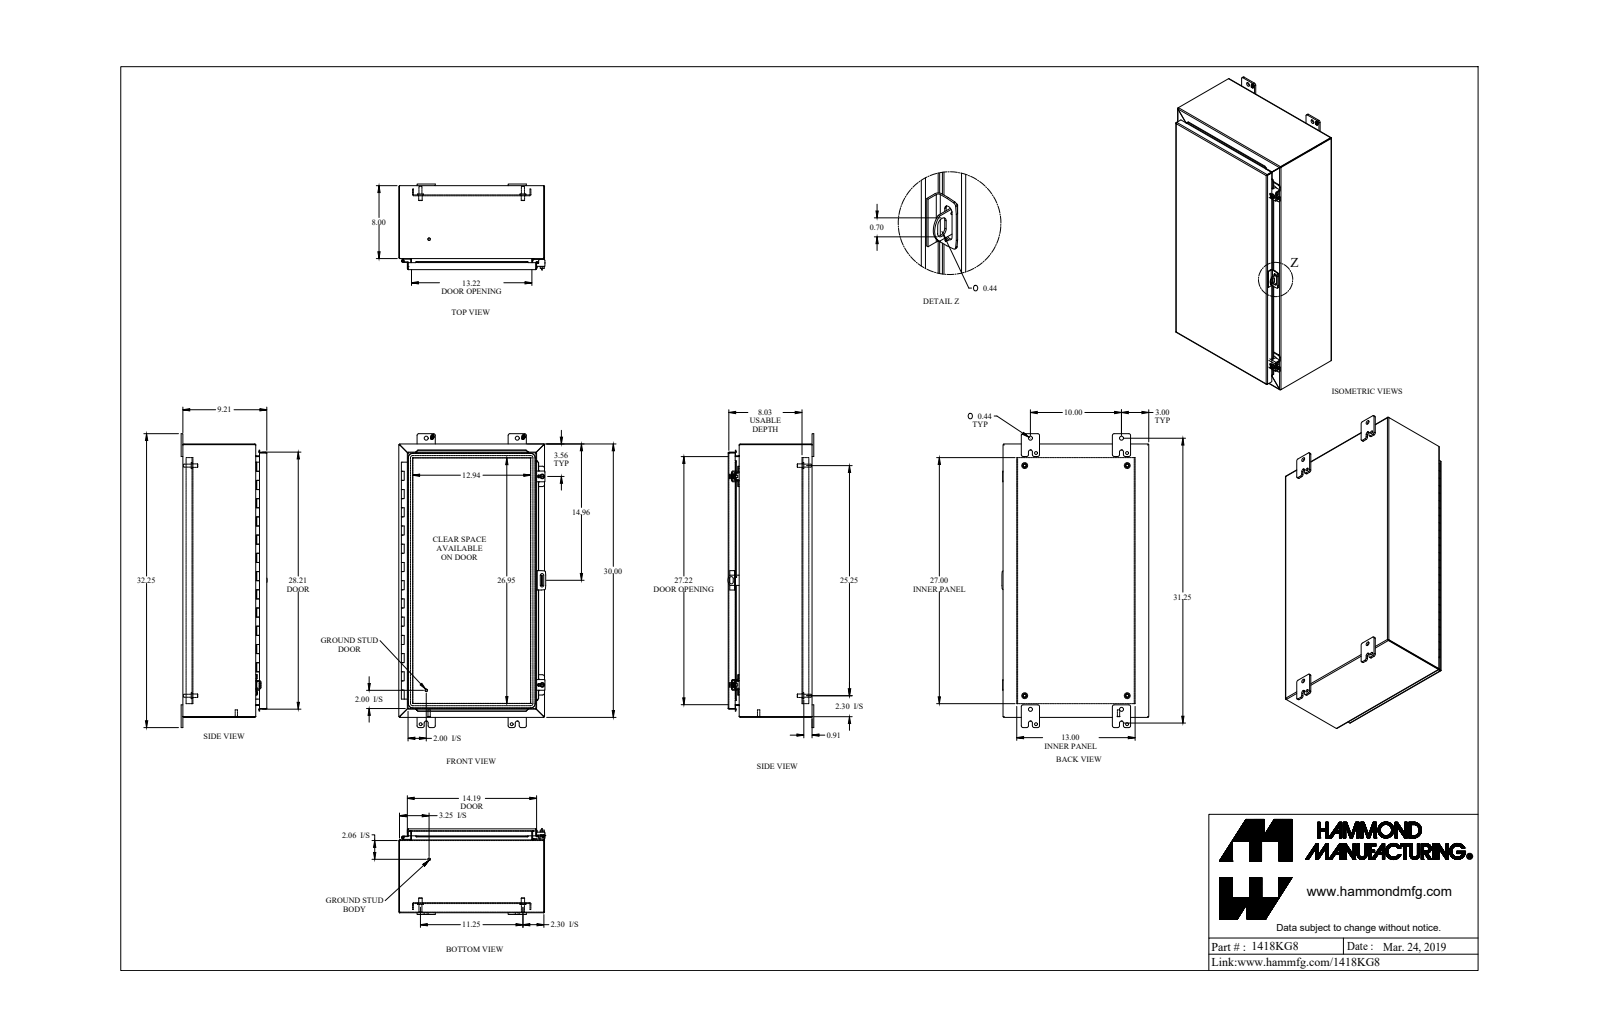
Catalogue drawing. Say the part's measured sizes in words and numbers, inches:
The part is named "1418KG8_Default". Its 3-D file was written by "SolidWorks 2019 (CONFIG_CONTROL_DESIGN)". It is 38 solids with 1209 faces: 739 planar, 402 cylindrical and 68 other. Overall it measures 32.25 by 16.125 by 9.437 inches. Its volume is 194 cubic inches and its surface area 5 040 square inches. Round holes: 4 of diameter 0.313, 4 of diameter 0.437, 4 of diameter 0.5, 2 of diameter 0.213, 2 of diameter 0.265, 2 of diameter 0.307, 2 of diameter 0.375, 2 of diameter 0.445, 1 of diameter 0.125, 1 of diameter 0.187. Round bosses or shafts: 4 of diameter 0.65, 4 of diameter 0.375, 4 of diameter 0.33, 2 of diameter 1, 2 of diameter 0.5, 2 of diameter 0.39, 2 of diameter 0.281, 2 of diameter 0.25. Partial cylindrical surfaces (rounded edges, fillets, slot ends): 26 of radius 0.188, 24 of radius 0.036, 24 of radius 0.108, 13 of radius 0.048, 13 of radius 0.143, 8 of radius 0.045, 8 of radius 0.218, 8 of radius 0.25. The main face-to-face distances are 0.072, 9.113, 9.041, 15.928, 0.937, 9.185, 0.095, 1.009, 8.081, 8.009. The hole center spacings are 1.736, 10, 11.25, 29.75, 31.386, 27.53, 27.643, 27.643.
